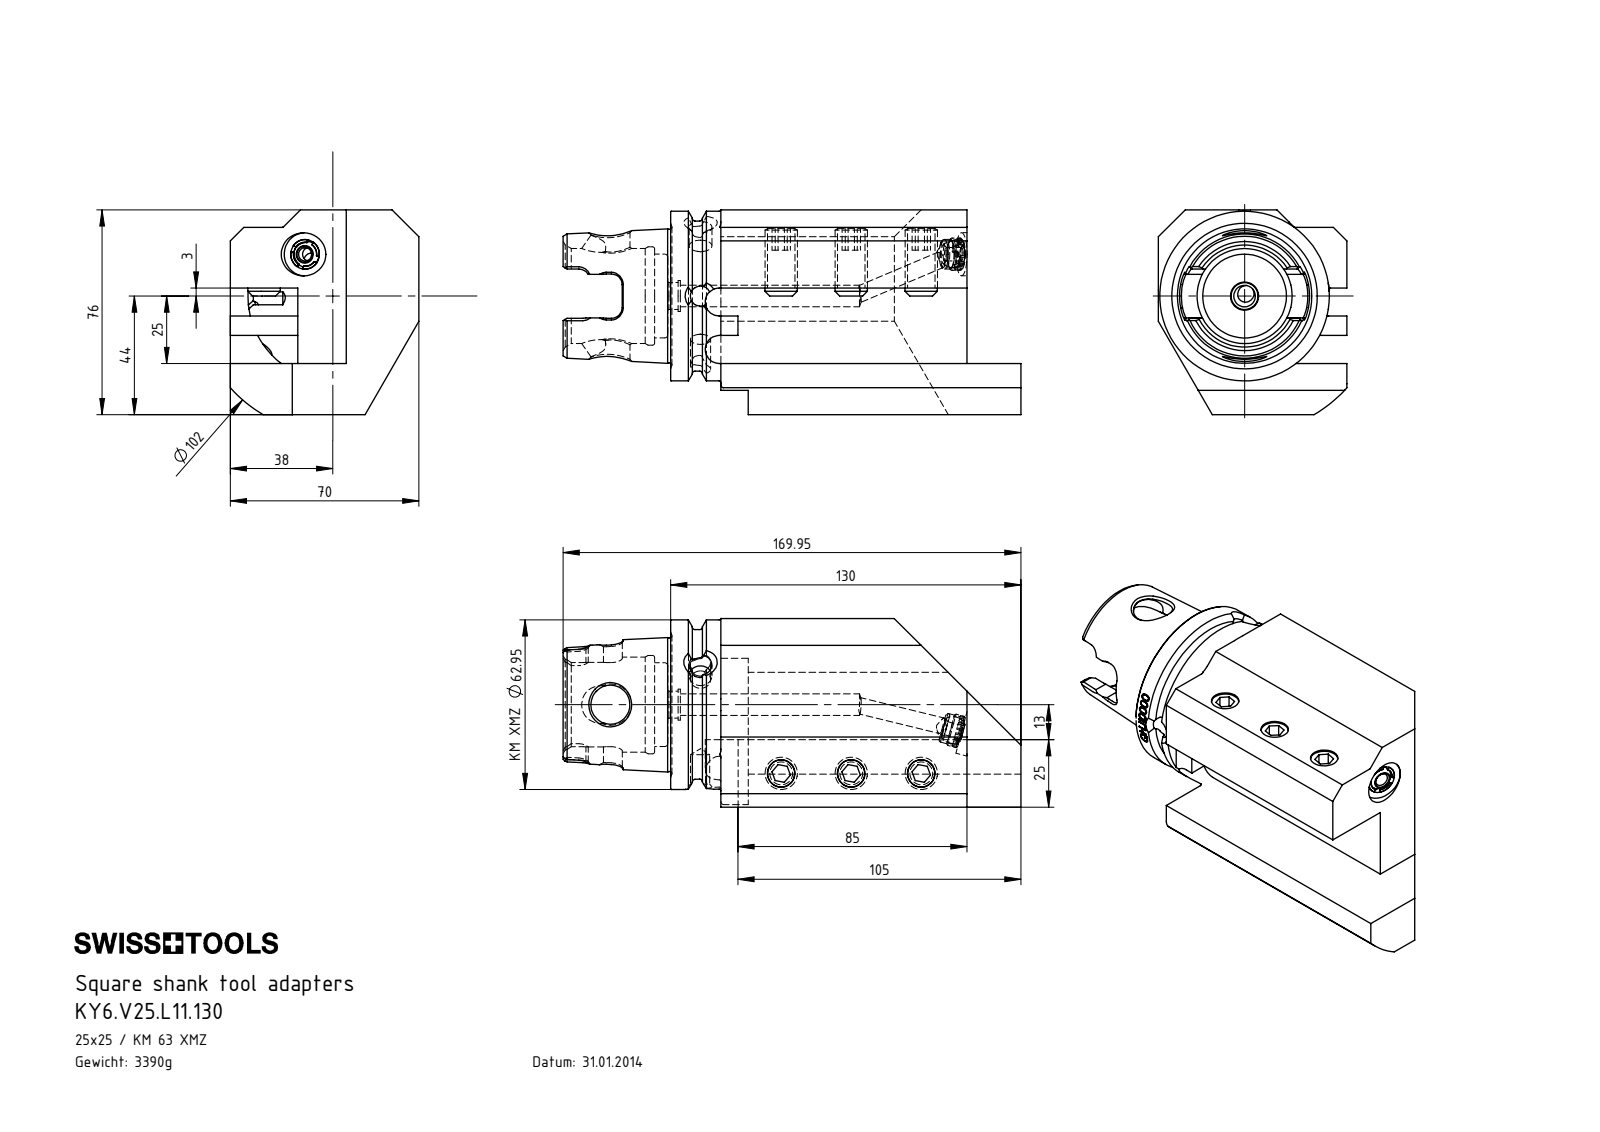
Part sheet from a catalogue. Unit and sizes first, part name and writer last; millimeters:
Units: millimetres
Overall size (bounding box): 169.95 × 76 × 70
Round holes (diameter × count): ⌀10.2 ×3, ⌀10 ×2, ⌀5 ×1, ⌀6 ×1, ⌀7.47 ×1, ⌀8 ×1, ⌀8.48 ×1, ⌀11 ×1, ⌀11.5 ×1, ⌀14.5 ×1, ⌀16 ×1, ⌀31.1 ×1
Round bosses / shafts (diameter × count): ⌀12 ×4, ⌀62.95 ×1, ⌀55.7 ×1
Partial cylindrical surfaces — rounded edges, fillets, slot ends (radius × count): R4 ×6, R5.2 ×2, R7.04 ×2, R0.5 ×1, R3.74 ×1, R4.4 ×1, R51 ×1
Main face-to-face distances: 25, 76, 19, 57, 47, 28, 29, 45, 70, 69.5
Hole centre spacings: 26, 52, 68.34, 92.97, 118.18
Volume: 431 829 mm³ · Surface area: 60 600 mm²
Bodies: 7 solids, 309 faces (104 planar, 77 cylindrical, 128 other)
Part name (STEP PRODUCT): KU1-U12.002.010; KY6-V25.L11.130_D_Ohne Beschriftung; KY6.V25.L11.130; ISO 4026 - M12 x 25 (+3 more)
STEP written by: SolidWorks 2017 (CONFIG_CONTROL_DESIGN)
